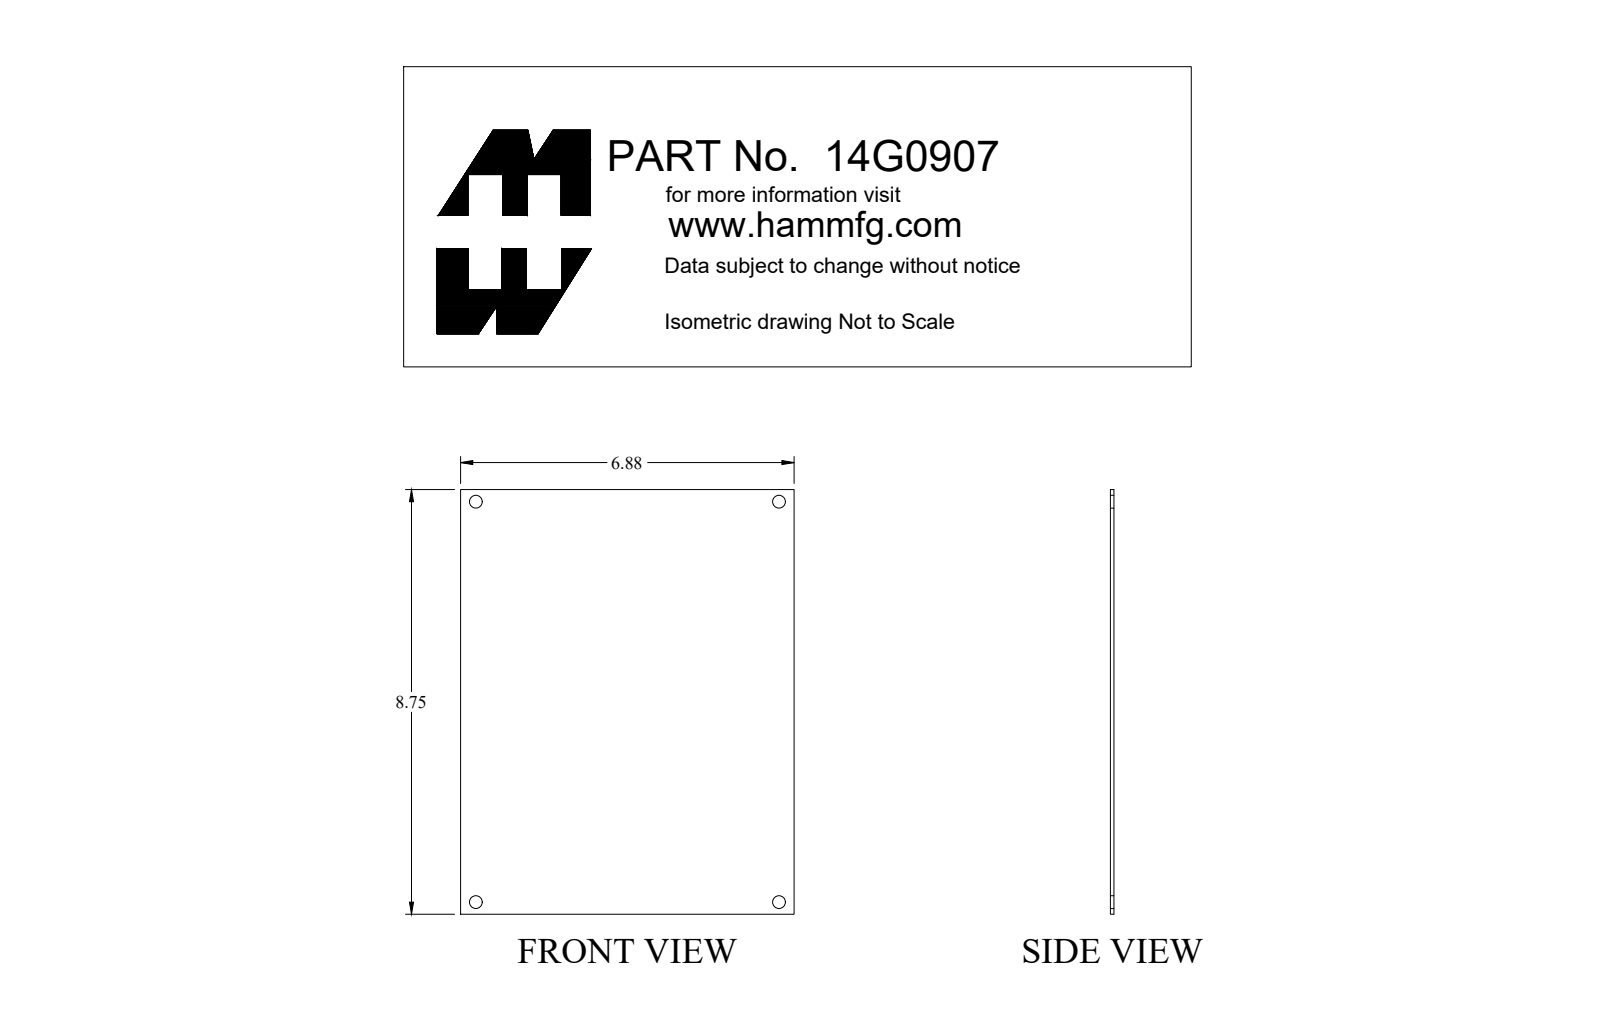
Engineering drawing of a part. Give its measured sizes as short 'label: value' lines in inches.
name: 14G0907
written by: SolidWorks 2018 (AUTOMOTIVE_DESIGN)
unit: in
bodies: 1 solid, 10 faces (6 planar, 4 cylindrical, 0 other)
size: 8.75 × 6.875 × 0.072
volume: 4.315 in³; area: 122.4 in²
holes: 4× ⌀0.265
face distances: 0.072, 6.875, 8.75
hole spacings: 6.25, 8.25, 10.35
